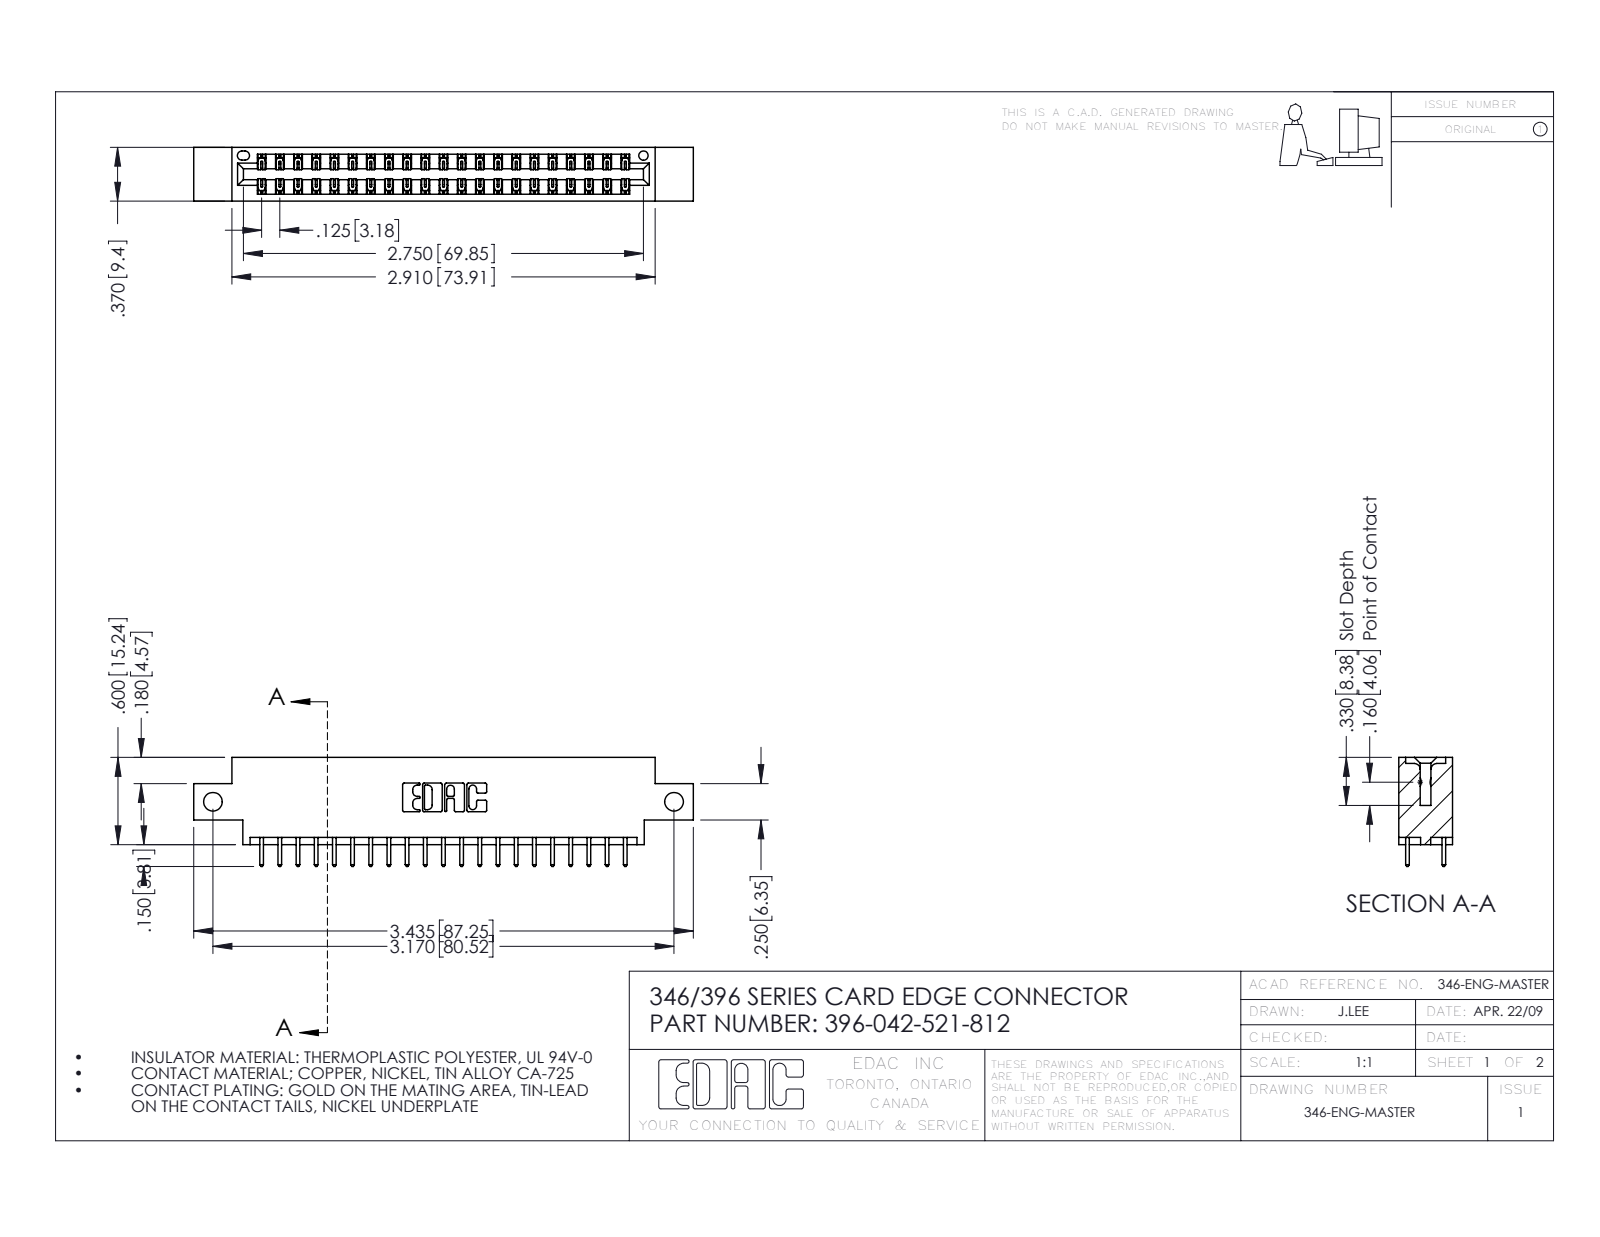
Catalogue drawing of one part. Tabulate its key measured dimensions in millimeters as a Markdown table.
| quantity | value |
| --- | --- |
| part name | 346 Part_0.170 Offset - Side Mount; 345-292-001_345-293-121; 396-042-521-812 |
| STEP written by | SolidWorks 2016 (CONFIG_CONTROL_DESIGN) |
| units | millimeters |
| bodies | 43 solids, 2310 faces (1550 planar, 760 cylindrical, 0 other) |
| overall size | 87.2 × 19.1 × 9.4 |
| volume | 8 080 mm³ |
| surface area | 10 710 mm² |
| round holes (diameter × count) | 3.3 × 2, 1.6 × 1 |
| partial cylindrical surfaces (radius × count) | 0.2 × 63, 0.3 × 42, 0.3 × 22, 0.2 × 6, 0.8 × 6, 0.7 × 3, 0.4 × 2, 0.6 × 2 |
| main face-to-face distances | 1.2, 8.2, 6.4, 9.4, 1.8, 7.6, 0.6, 7, 3.8, 5.6 |
| hole center spacings | 80.5 |
